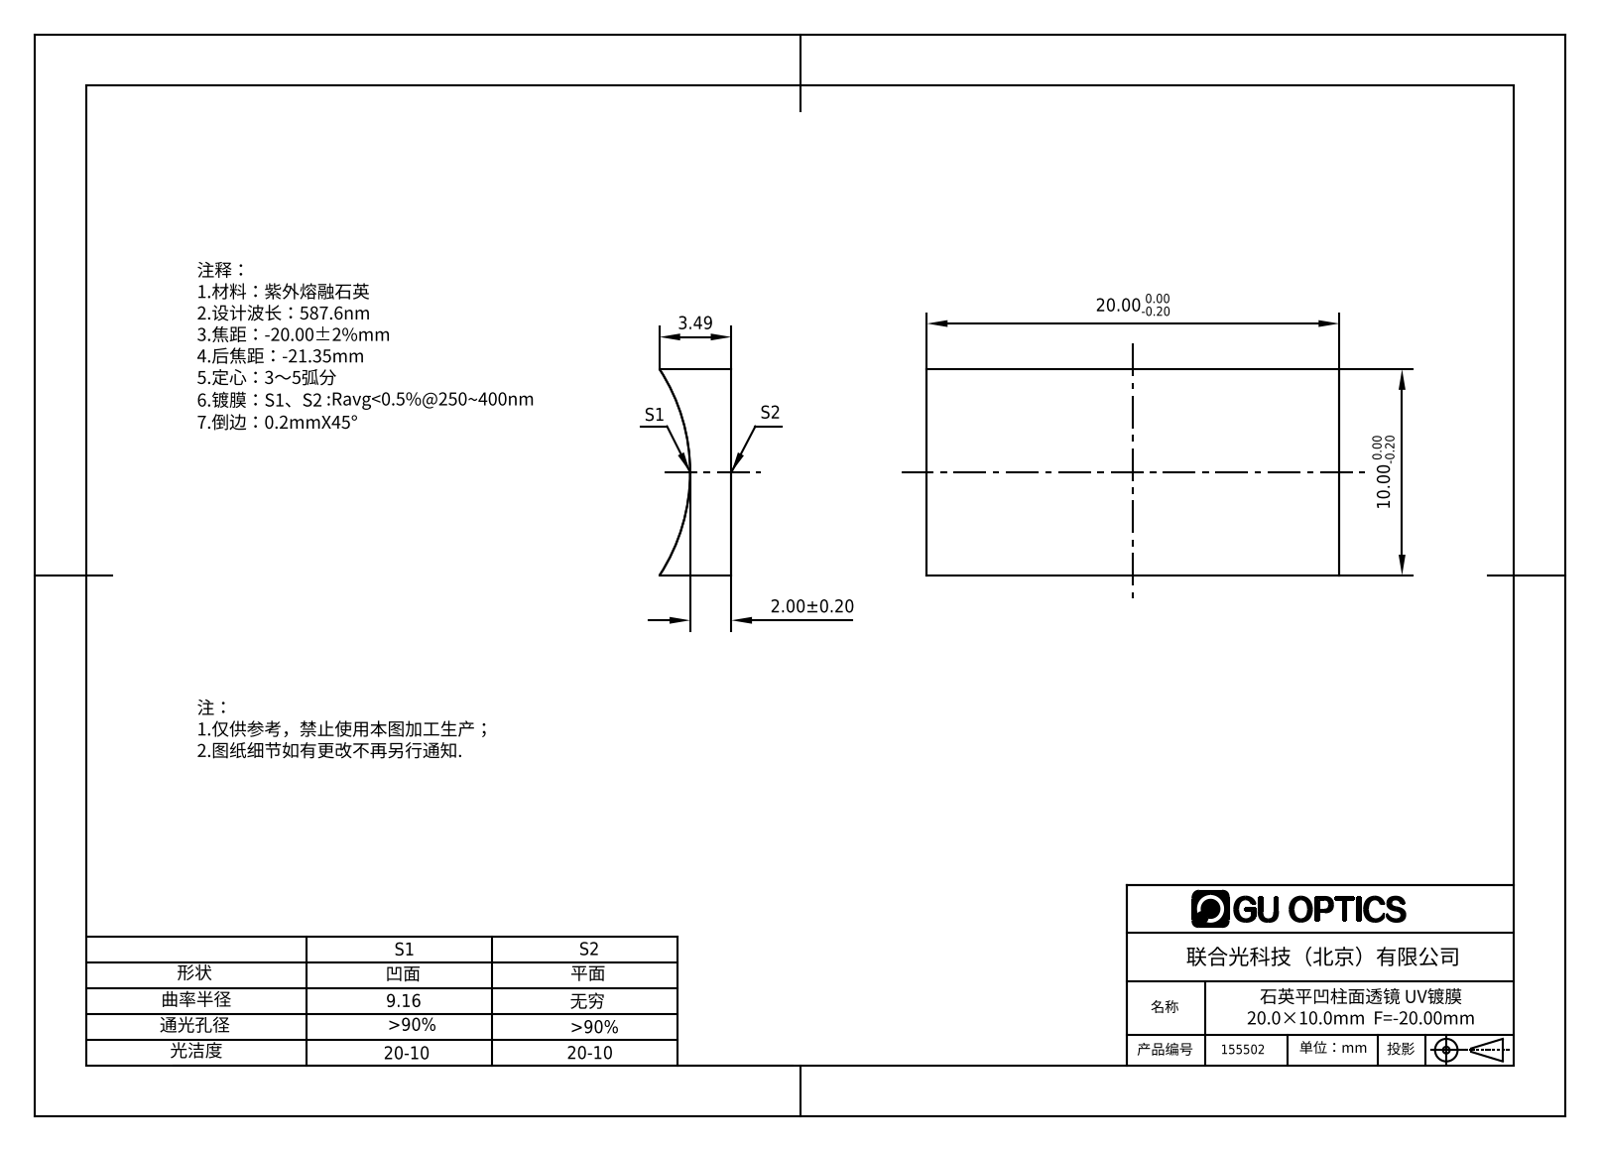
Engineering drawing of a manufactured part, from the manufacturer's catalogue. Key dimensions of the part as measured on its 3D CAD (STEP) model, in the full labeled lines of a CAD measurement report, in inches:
Part name (STEP PRODUCT): 155476
STEP written by: SolidWorks 2016 (AUTOMOTIVE_DESIGN)
Units: inches
Bodies: 1 solid, 6 faces (5 planar, 1 cylindrical, 0 other)
Overall size (bounding box): 0.787 × 0.394 × 0.137
Volume: 0.03 in³ · Surface area: 0.932 in²
Partial cylindrical surfaces — rounded edges, fillets, slot ends (radius × count): R0.361 ×1
Main face-to-face distances: 0.394, 0.787
